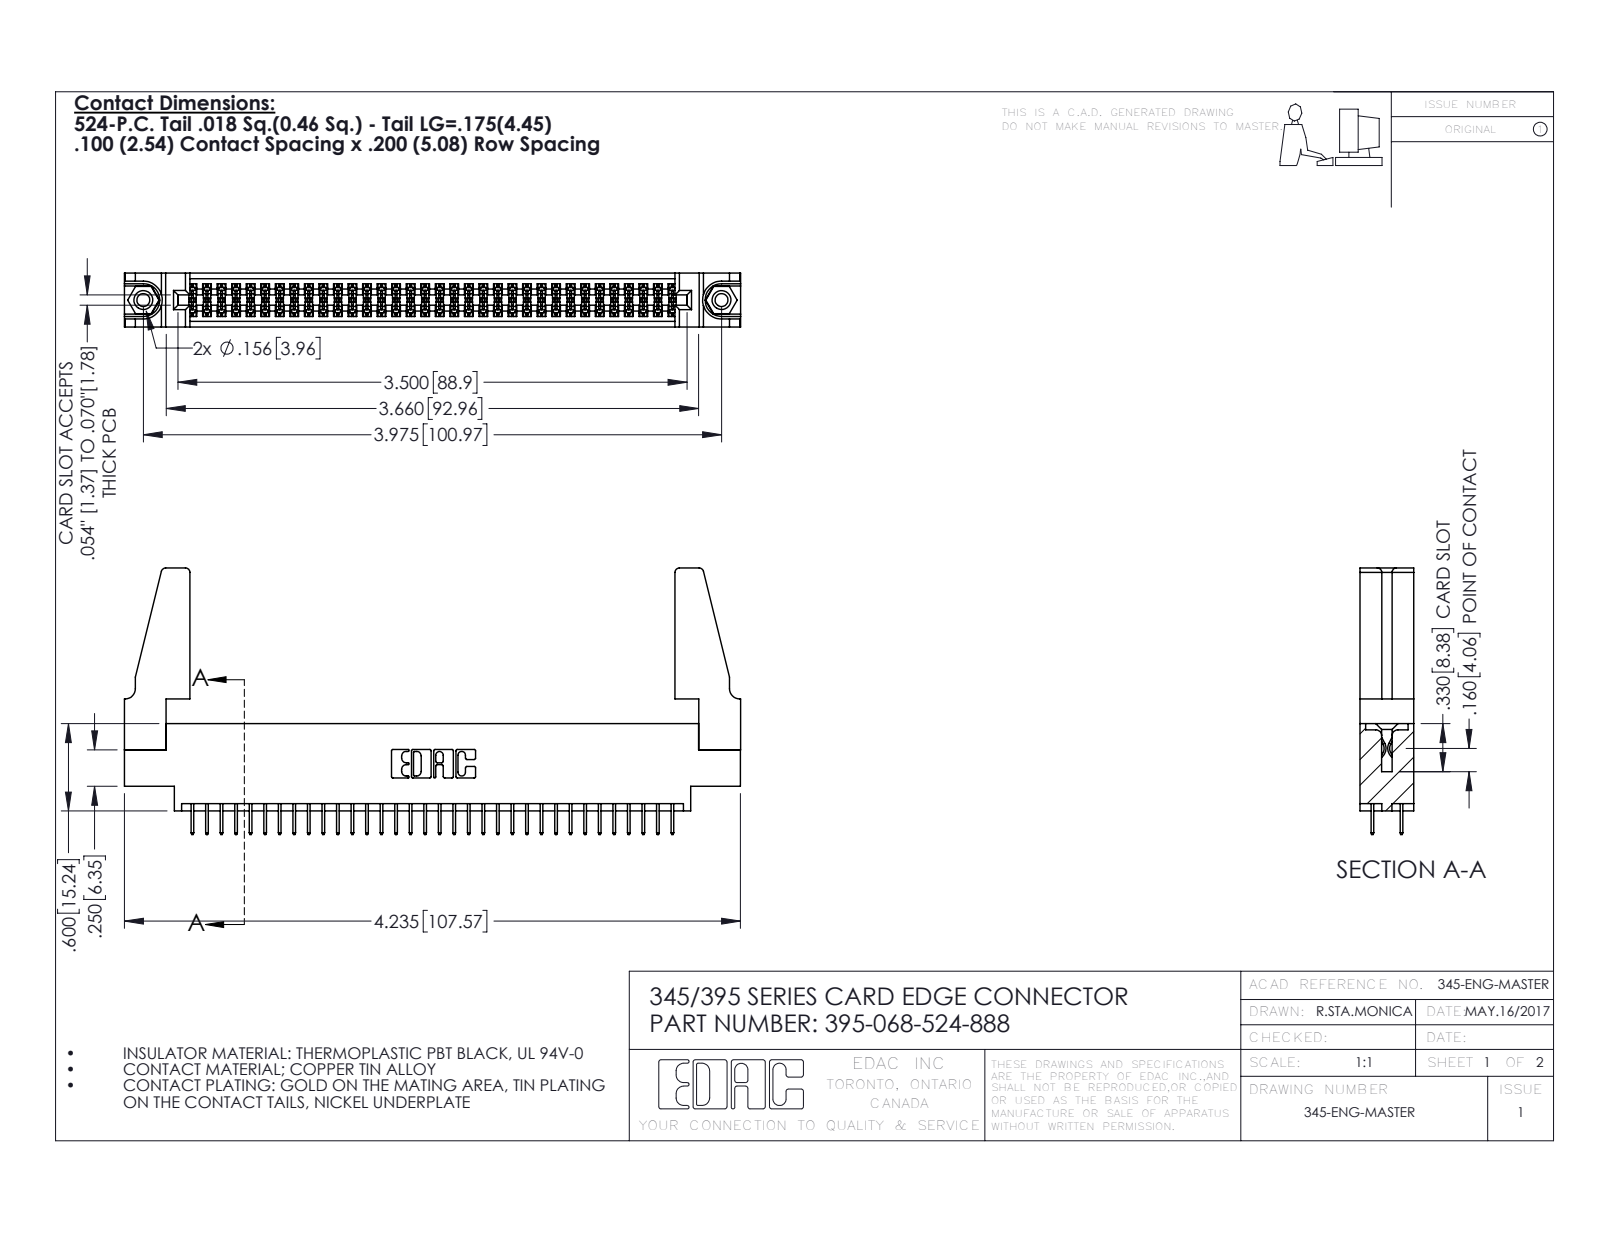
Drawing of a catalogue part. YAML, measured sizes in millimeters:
part_name: "345-292-001_345-293-124; 395-068-524-888; 345-220-078_345-220-088; 345 Part_0.170 Offset - 0.156 Dia-TH (+1 more)"
step_written_by: "SolidWorks 2016 (CONFIG_CONTROL_DESIGN)"
units: millimeters
bodies: {solids: 73, faces: 3926, planar: 2808, cylindrical: 1102, other: 16}
overall_size: [107.6, 46.5, 9.4]
volume: 13400
surface_area: 17860
round_holes:
  - {diameter: 2.3, count: 2}
  - {diameter: 3.2, count: 2}
  - {diameter: 4, count: 2}
  - {diameter: 1.6, count: 1}
round_bosses_or_shafts:
  - {diameter: 3.9, count: 2}
partial_cylinders:
  - {radius: 0.2, count: 102}
  - {radius: 0.3, count: 22}
  - {radius: 0.8, count: 8}
  - {radius: 0.2, count: 6}
  - {radius: 0.8, count: 6}
  - {radius: 0.7, count: 3}
  - {radius: 0.4, count: 2}
  - {radius: 0.5, count: 2}
face_to_face_distances: [1.8, 9.4, 7.6, 5.1, 2.5, 6.9, 0.6, 5.7, 4.4, 1.8]
hole_center_spacings: [6.9, 95, 101]
